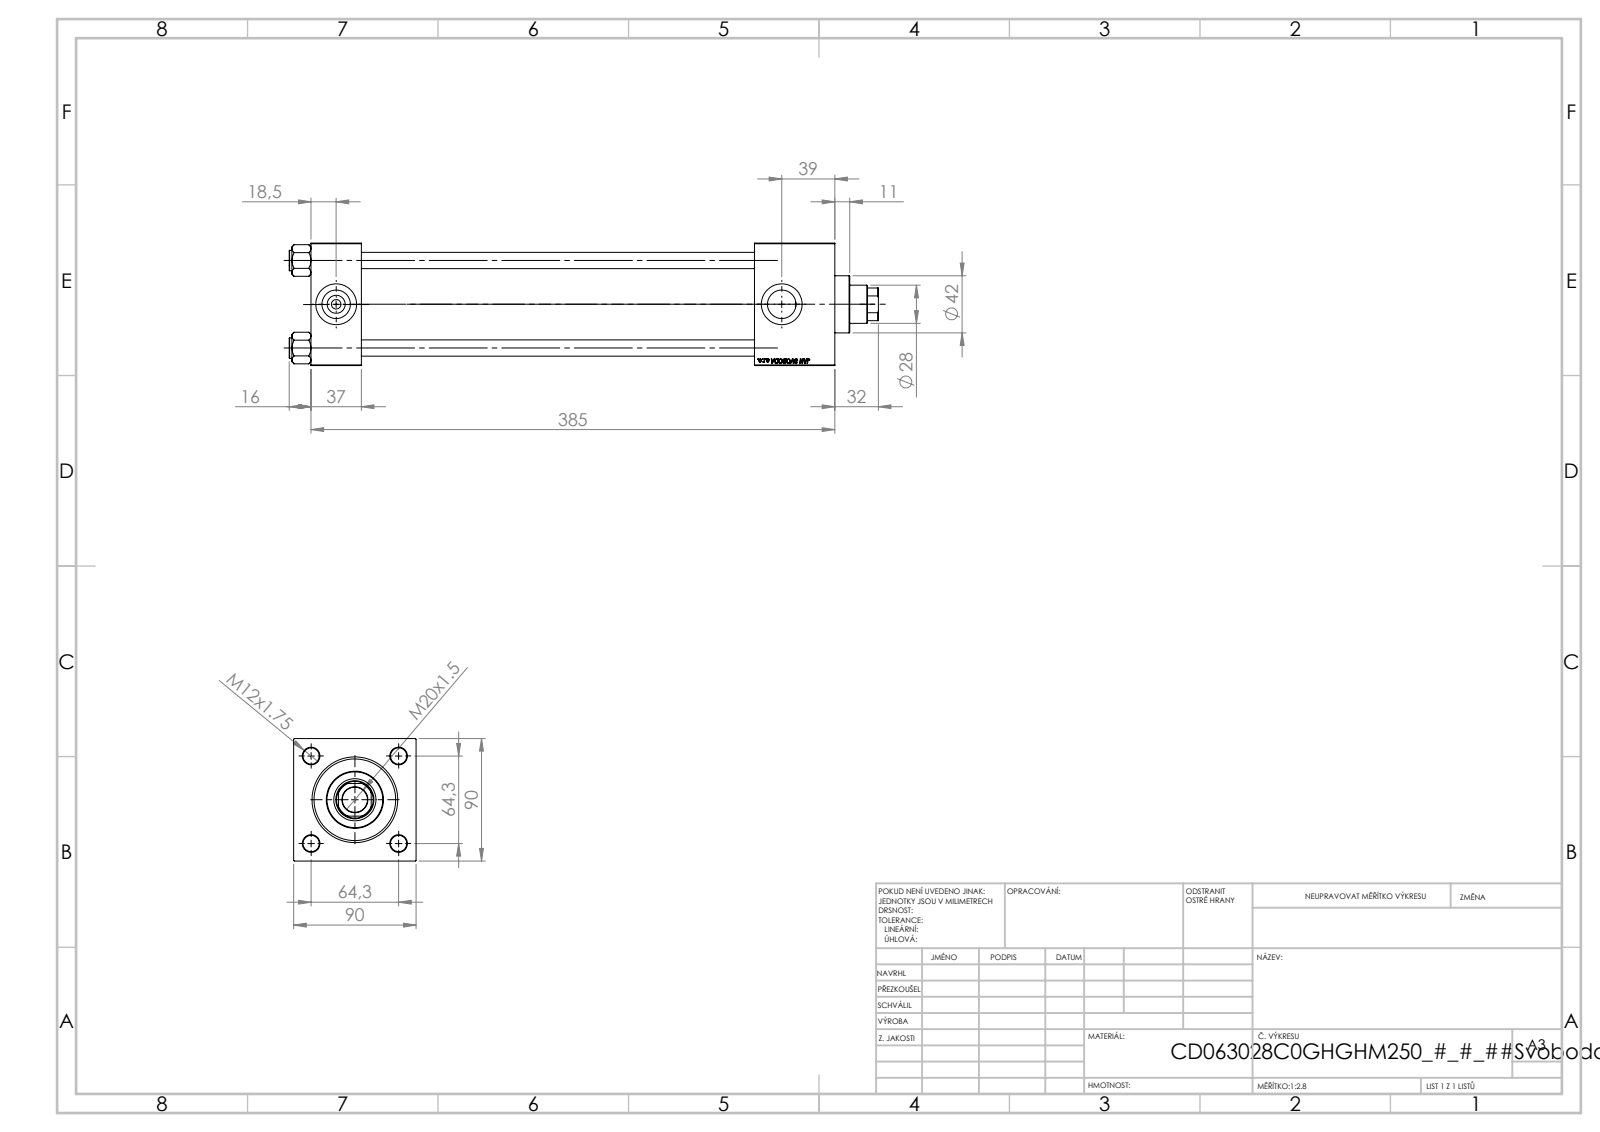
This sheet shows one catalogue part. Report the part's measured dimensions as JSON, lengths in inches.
{"part_name": "NUT_M5_V215CD_C; V215CD_Body_C; V215CD_C_TYCINKA; V215CD_VCP_C (+1 more)", "step_written_by": "SolidWorks 2019 (CONFIG_CONTROL_DESIGN)", "units": "inches", "bodies": {"solids": 11, "faces": 1148, "planar": 526, "cylindrical": 86, "other": 536}, "overall_size": [17.047, 3.543, 3.543], "volume_in3": 81.53, "surface_area_in2": 510.6, "round_holes": [[0.472, 4], [0.276, 2], [0.825, 2], [1.181, 2], [0.728, 1], [1.102, 1], [1.22, 1], [1.969, 1], [2.362, 1], [2.48, 1]], "round_bosses_or_shafts": [[0.591, 4], [2.717, 1], [1.654, 1]], "partial_cylinders_radius": [[0.531, 1]], "face_to_face_distances": [3.543, 1.457, 15.157, 13.701, 12.835, 11.378, 2.323, 14.028, 12.571, 1.193], "hole_center_spacings": [1.79, 2.531, 3.58, 12.894]}
